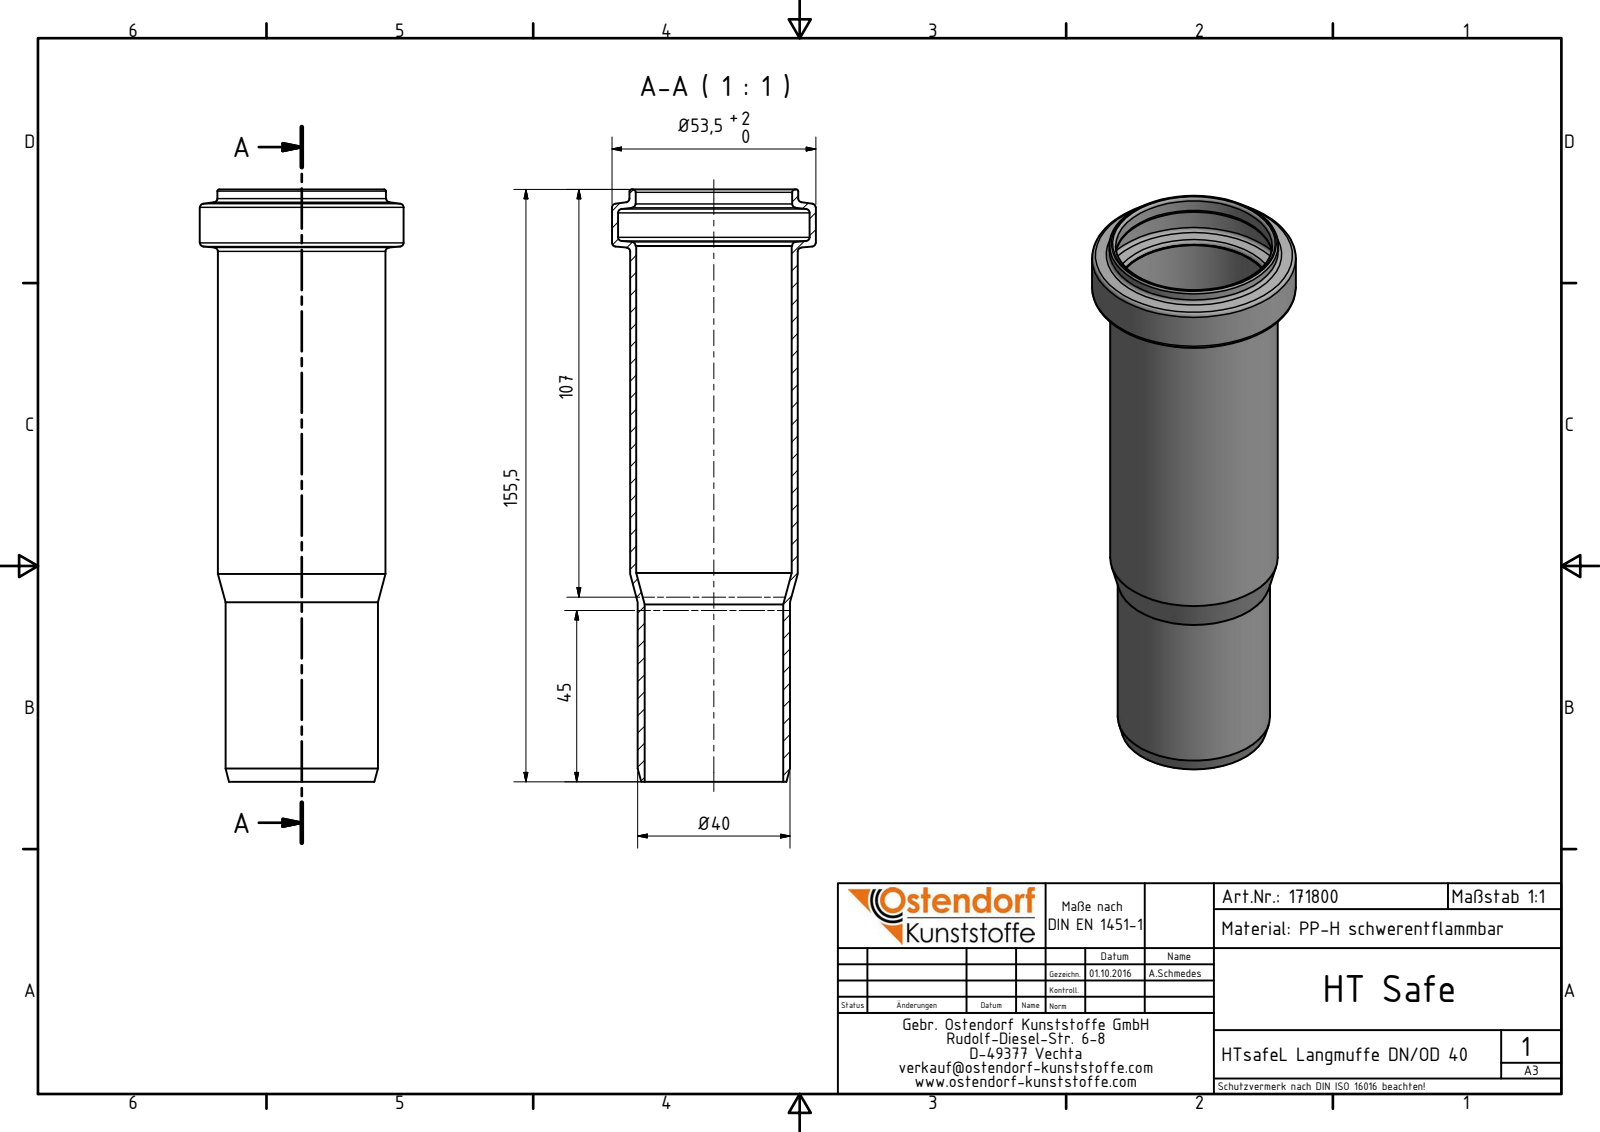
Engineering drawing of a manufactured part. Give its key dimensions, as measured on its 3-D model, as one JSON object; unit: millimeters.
{"part_name": "171800 HTsafeL DN_OD 40", "step_written_by": "Autodesk Inventor 2016 (AUTOMOTIVE_DESIGN)", "units": "millimeters", "bodies": {"solids": 1, "faces": 29, "planar": 3, "cylindrical": 9, "other": 17}, "overall_size": [155.5, 53.5, 53.5], "volume_mm3": 35492, "surface_area_mm2": 43120, "round_holes": [[36.4, 1], [40.8, 1], [41.1, 1], [50.3, 1]], "round_bosses_or_shafts": [[53.5, 1], [44.3, 1], [44, 1], [40, 1]], "face_to_face_distances": [155.5, 140.6, 14.9]}
